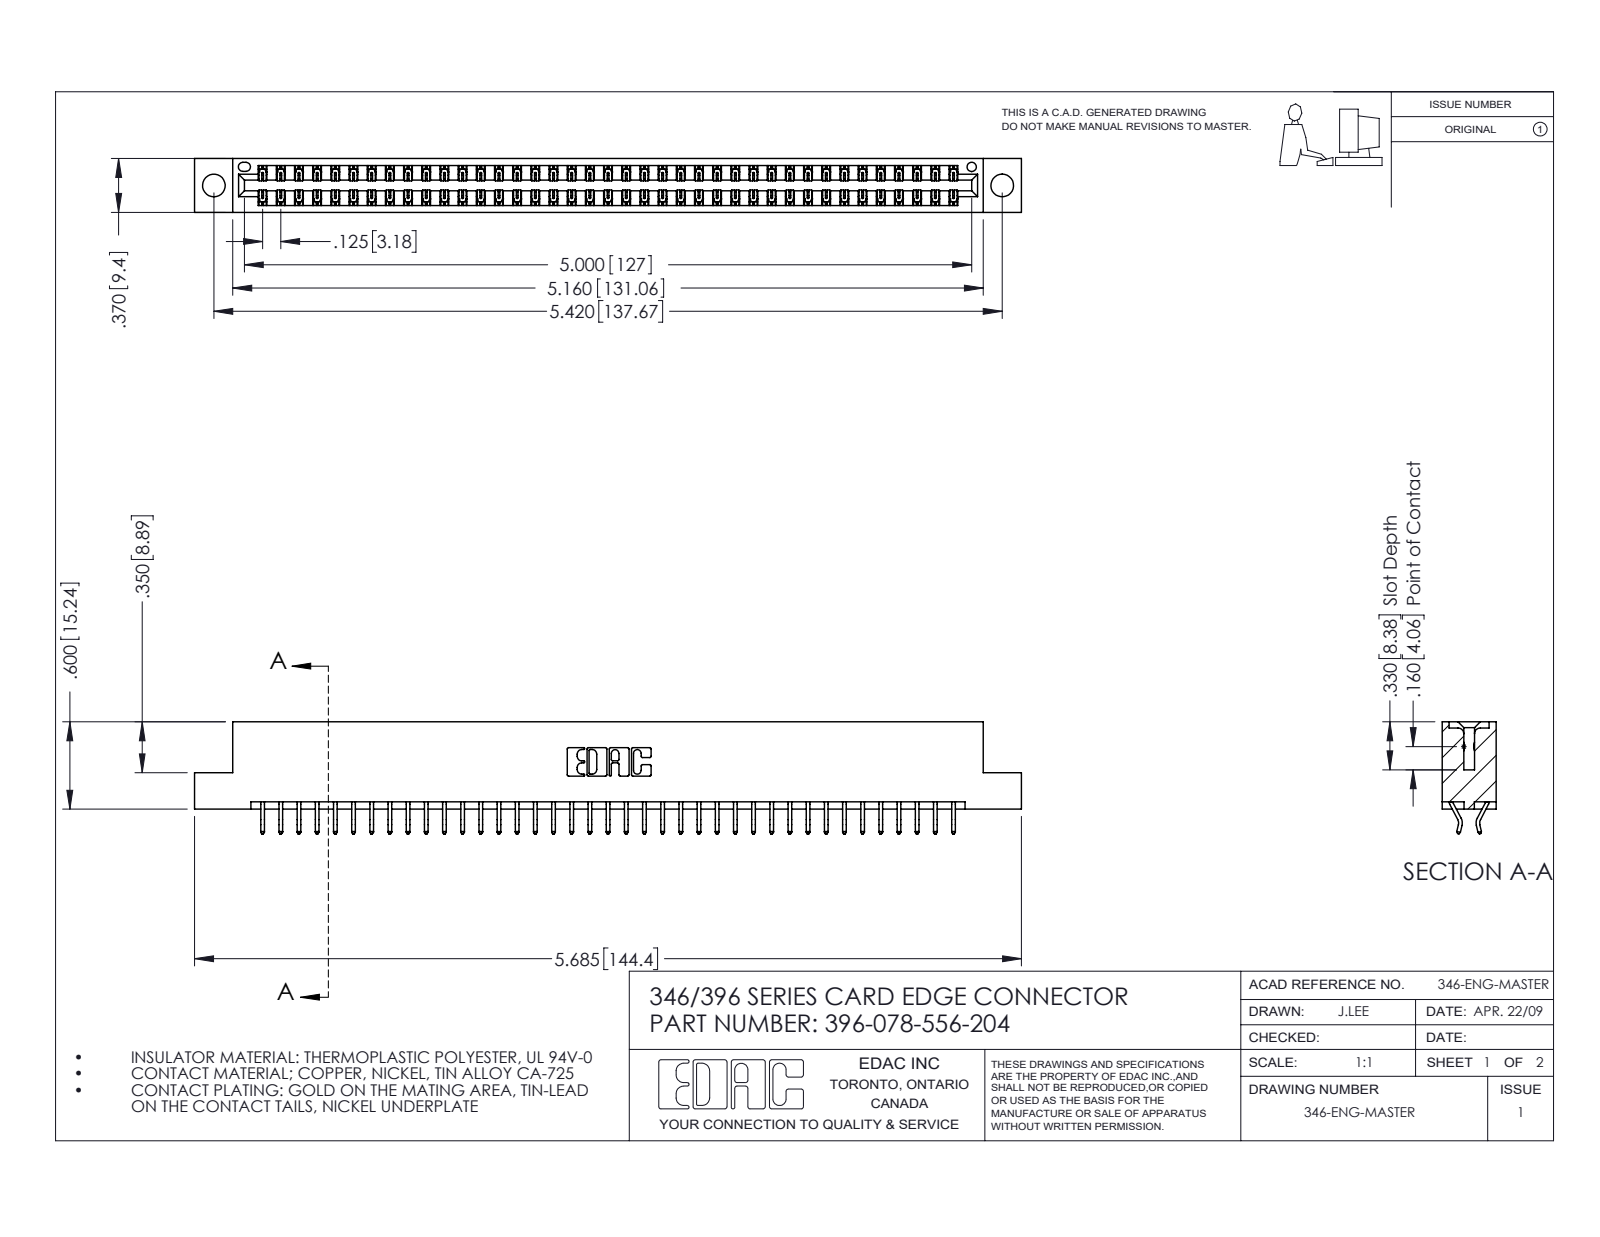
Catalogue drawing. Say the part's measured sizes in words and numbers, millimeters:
The part is named "345-292-001_556 Tail; 396-078-556-204; 346 Part_Flush Mounting Lugs - 0.156 Dia-TH". Its 3-D file was written by "SolidWorks 2016 (CONFIG_CONTROL_DESIGN)". It is 79 solids with 4646 faces: 3118 planar, 1528 cylindrical and 0 other. Overall it measures 144.4 by 19.6 by 9.4 millimeters. Its volume is 14 000 cubic millimeters and its surface area 18 890 square millimeters. Round holes: 2 of diameter 4, 1 of diameter 1.6. Partial cylindrical surfaces (rounded edges, fillets, slot ends): 117 of radius 0.2, 22 of radius 0.3, 6 of radius 0.2, 6 of radius 0.8, 3 of radius 0.7, 2 of radius 0.3, 2 of radius 0.4, 2 of radius 0.6. The main face-to-face distances are 1.2, 8.2, 9.4, 6.4, 0.6, 1.8, 7.6, 7, 3.8, 5.6. The hole center spacings are 6.2, 132.4, 137.7.
